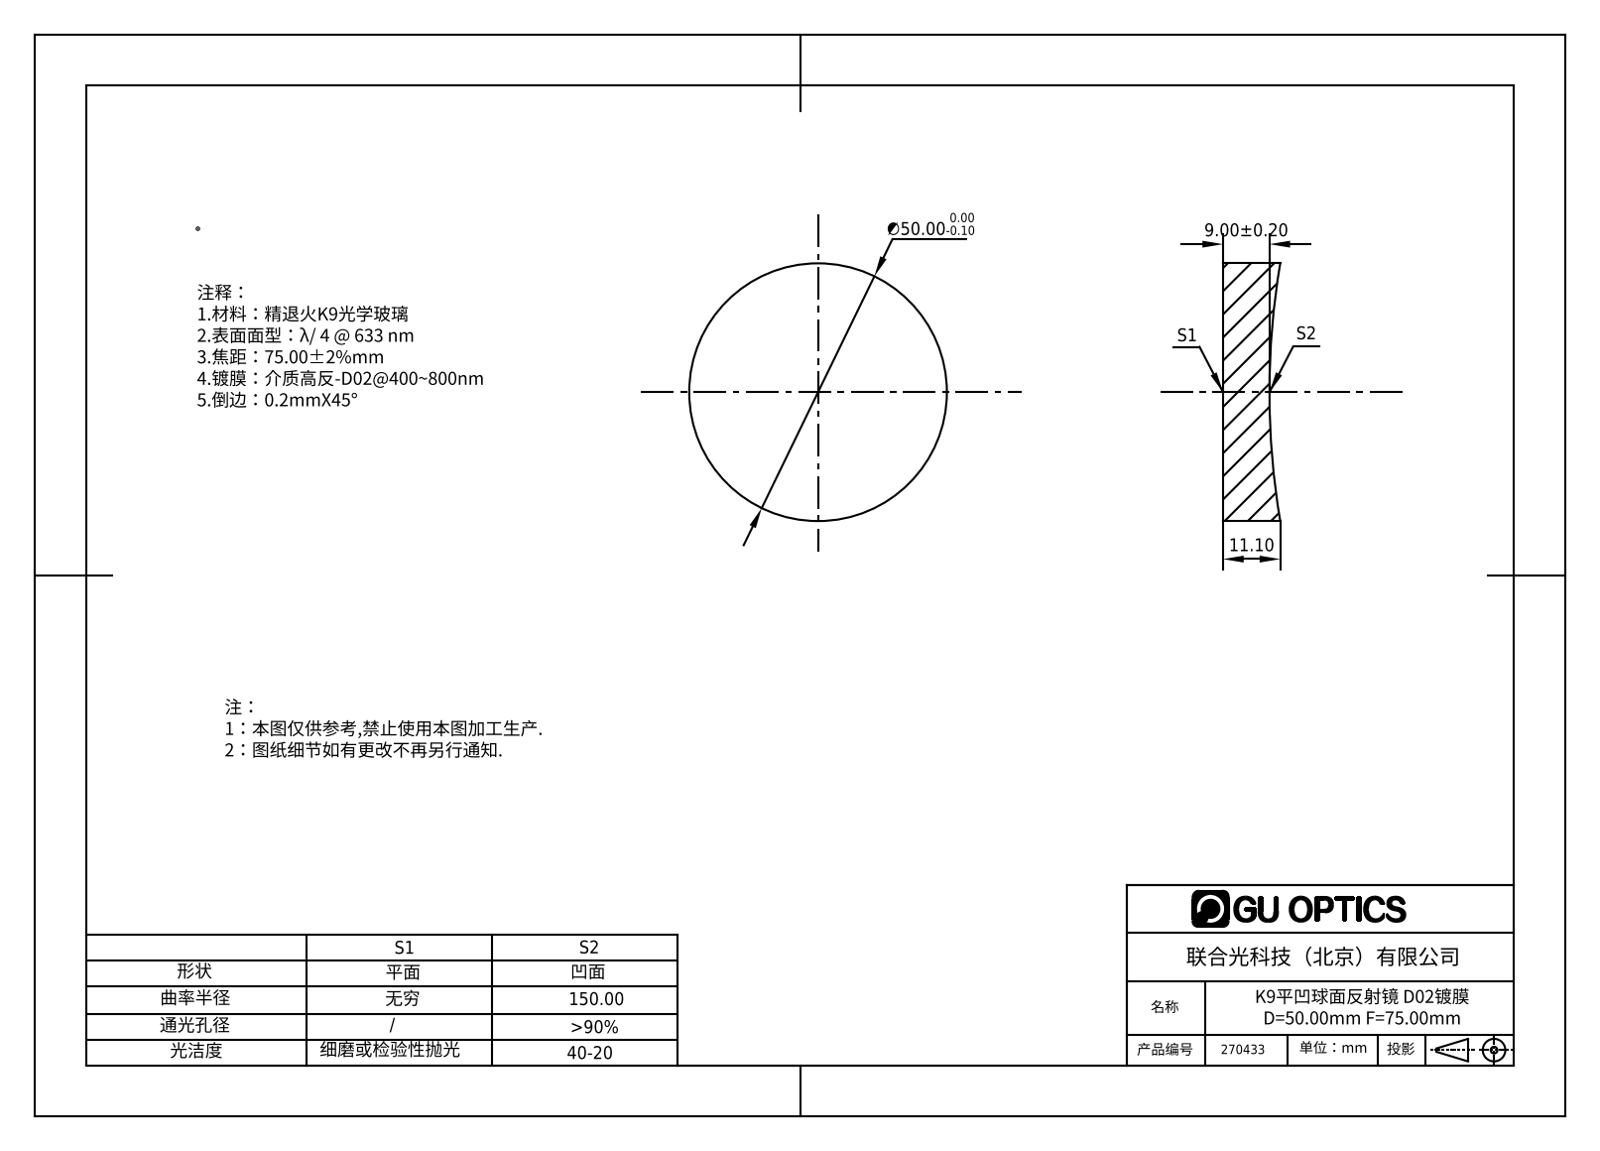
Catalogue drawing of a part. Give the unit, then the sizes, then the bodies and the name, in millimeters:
Units: millimetres
Overall size (bounding box): 50 × 50 × 11.1
Round bosses / shafts (diameter × count): ⌀50 ×1
Volume: 19 726 mm³ · Surface area: 5 684 mm²
Bodies: 1 solid, 5 faces (1 planar, 2 cylindrical, 2 other)
Part name (STEP PRODUCT): 270043
STEP written by: SolidWorks 2016 (AUTOMOTIVE_DESIGN)
